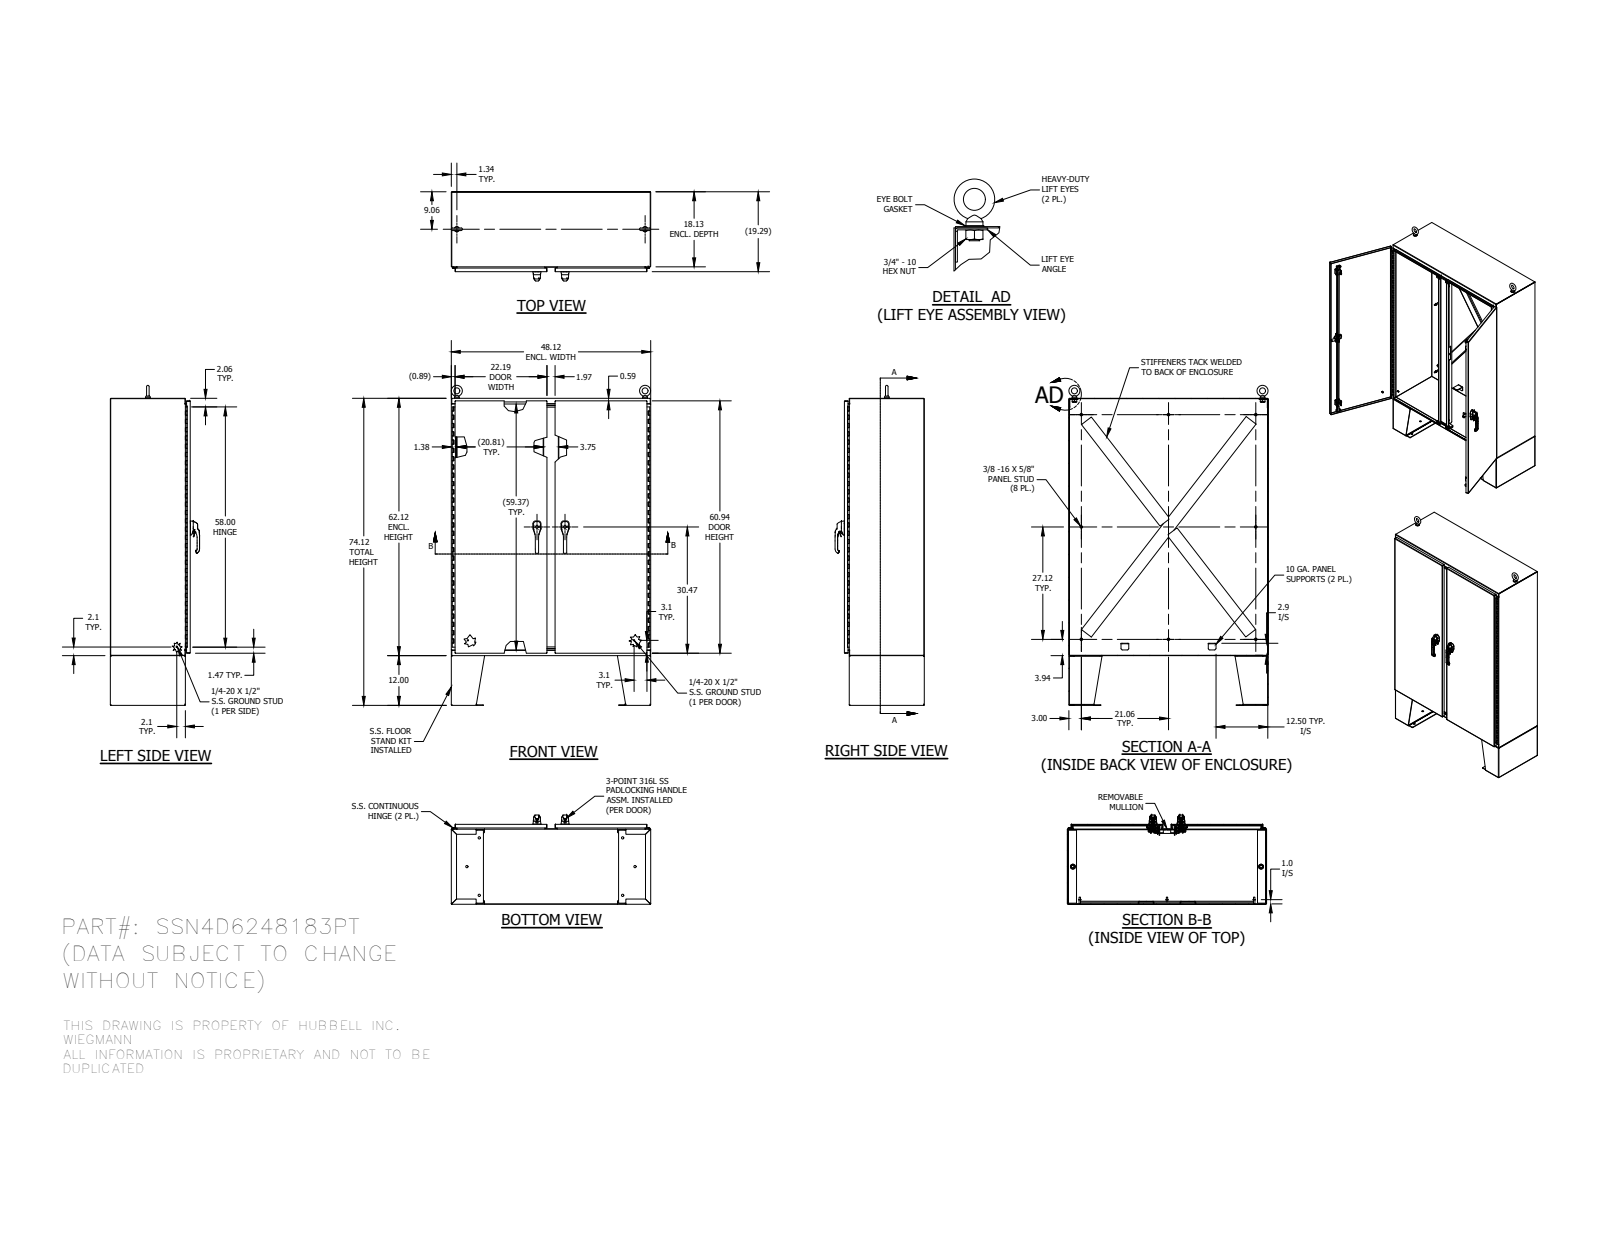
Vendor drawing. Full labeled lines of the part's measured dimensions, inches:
Part name (STEP PRODUCT): HFW369101_1; SSFK1218_1; 328131T-58_1; HFW3026_1 (+8 more)
STEP written by: SolidWorks 2014 (AUTOMOTIVE_DESIGN)
Units: inches
Bodies: 138 solids, 7184 faces (2696 planar, 2772 cylindrical, 1716 other)
Overall size (bounding box): 77.248 × 48.125 × 21.538
Volume: 1 323 in³ · Surface area: 27 427 in²
Round holes (diameter × count): ⌀0.563 ×18, ⌀0.262 ×16, ⌀0.375 ×16, ⌀0.187 ×8, ⌀0.213 ×6, ⌀0.281 ×6, ⌀0.25 ×5, ⌀0.196 ×4, ⌀0.241 ×4, ⌀0.252 ×4, ⌀0.281 ×4, ⌀0.315 ×4
Round bosses / shafts (diameter × count): ⌀0.33 ×10, ⌀0.625 ×8, ⌀0.25 ×7, ⌀0.533 ×6, ⌀0.236 ×6, ⌀1 ×5, ⌀0.563 ×4, ⌀0.531 ×4
Partial cylindrical surfaces — rounded edges, fillets, slot ends (radius × count): R0.02 ×342, R0.012 ×213, R0.125 ×46, R0.019 ×42, R0.05 ×34, R0.031 ×32, R0.079 ×28, R0.025 ×24
Main face-to-face distances: 0.094, 19.196, 19.193, 48.031, 62.031, 19.102, 19.1, 19.29, 0.096, 19.287
Hole centre spacings: 6.444, 0.38, 0.38, 0.76, 12.889, 46.321, 52.052, 52.427
